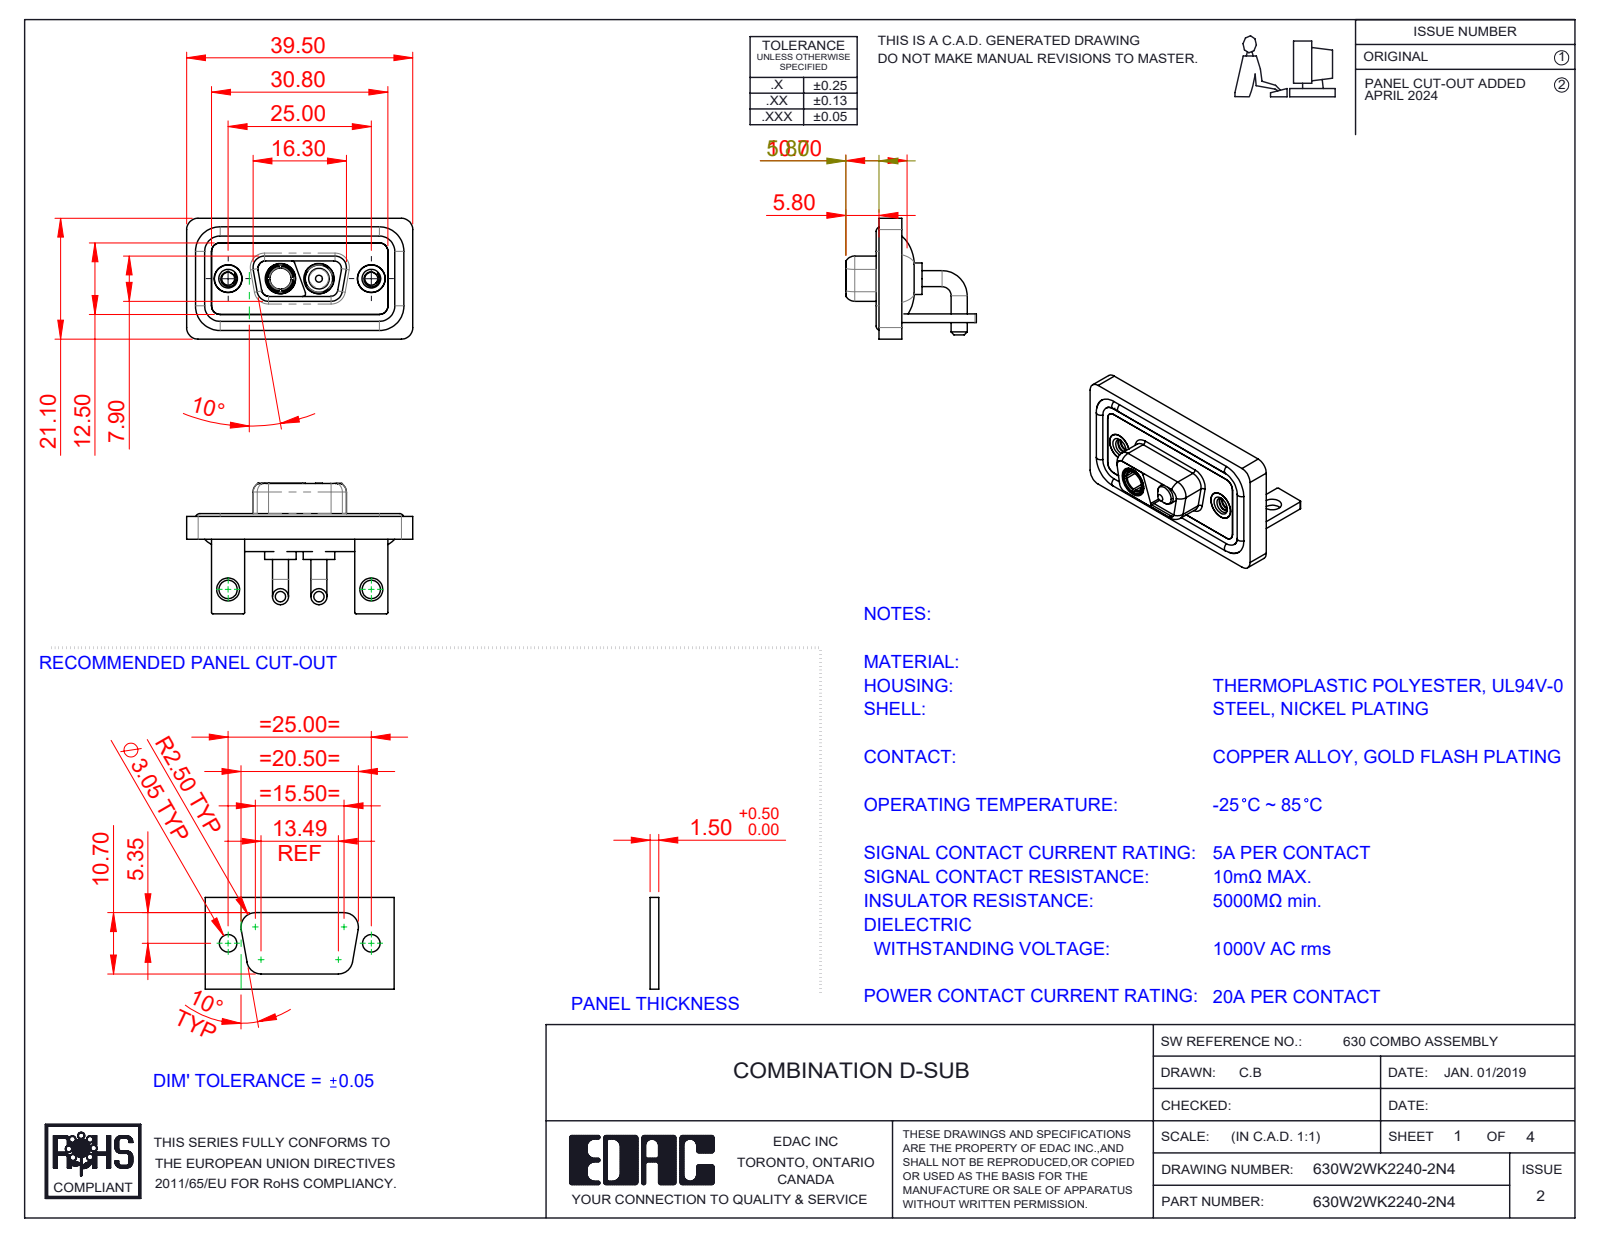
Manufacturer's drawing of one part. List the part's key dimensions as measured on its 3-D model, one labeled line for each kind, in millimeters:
Part name (STEP PRODUCT): 630Combo Shell Rear_09 Contacts; 630Combo Waterproof Housing_09 Contacts; 630Combo Threaded Rivet_2; 630Combo Shell Front_09 Contacts (+5 more)
STEP written by: SolidWorks 2023 (CONFIG_CONTROL_DESIGN)
Units: millimetres
Bodies: 13 solids, 556 faces (164 planar, 259 cylindrical, 133 other)
Overall size (bounding box): 39.5 × 22.8 × 21.1
Volume: 5 073 mm³ · Surface area: 8 229 mm²
Round holes (diameter × count): ⌀4.85 ×4, ⌀2.26 ×2, ⌀3.2 ×2, ⌀4 ×2, ⌀4.05 ×2, ⌀5 ×2, ⌀5.3 ×2, ⌀3.7 ×1
Round bosses / shafts (diameter × count): ⌀2.8 ×4, ⌀1.6 ×4, ⌀5.5 ×2, ⌀5.2 ×2, ⌀4.95 ×2, ⌀4.8 ×2, ⌀4.75 ×2, ⌀3.75 ×2
Partial cylindrical surfaces — rounded edges, fillets, slot ends (radius × count): R2 ×19, R1.5 ×18, R0.25 ×16, R1.35 ×8, R1.6 ×8, R0.5 ×7, R0.6 ×4, R0.65 ×4
Main face-to-face distances: 0.4, 2.9, 1.5, 1.1, 3.7, 1.8, 0.8, 2.5, 1.6, 3.1
Hole centre spacings: 9.14, 15.86, 25, 6.72
